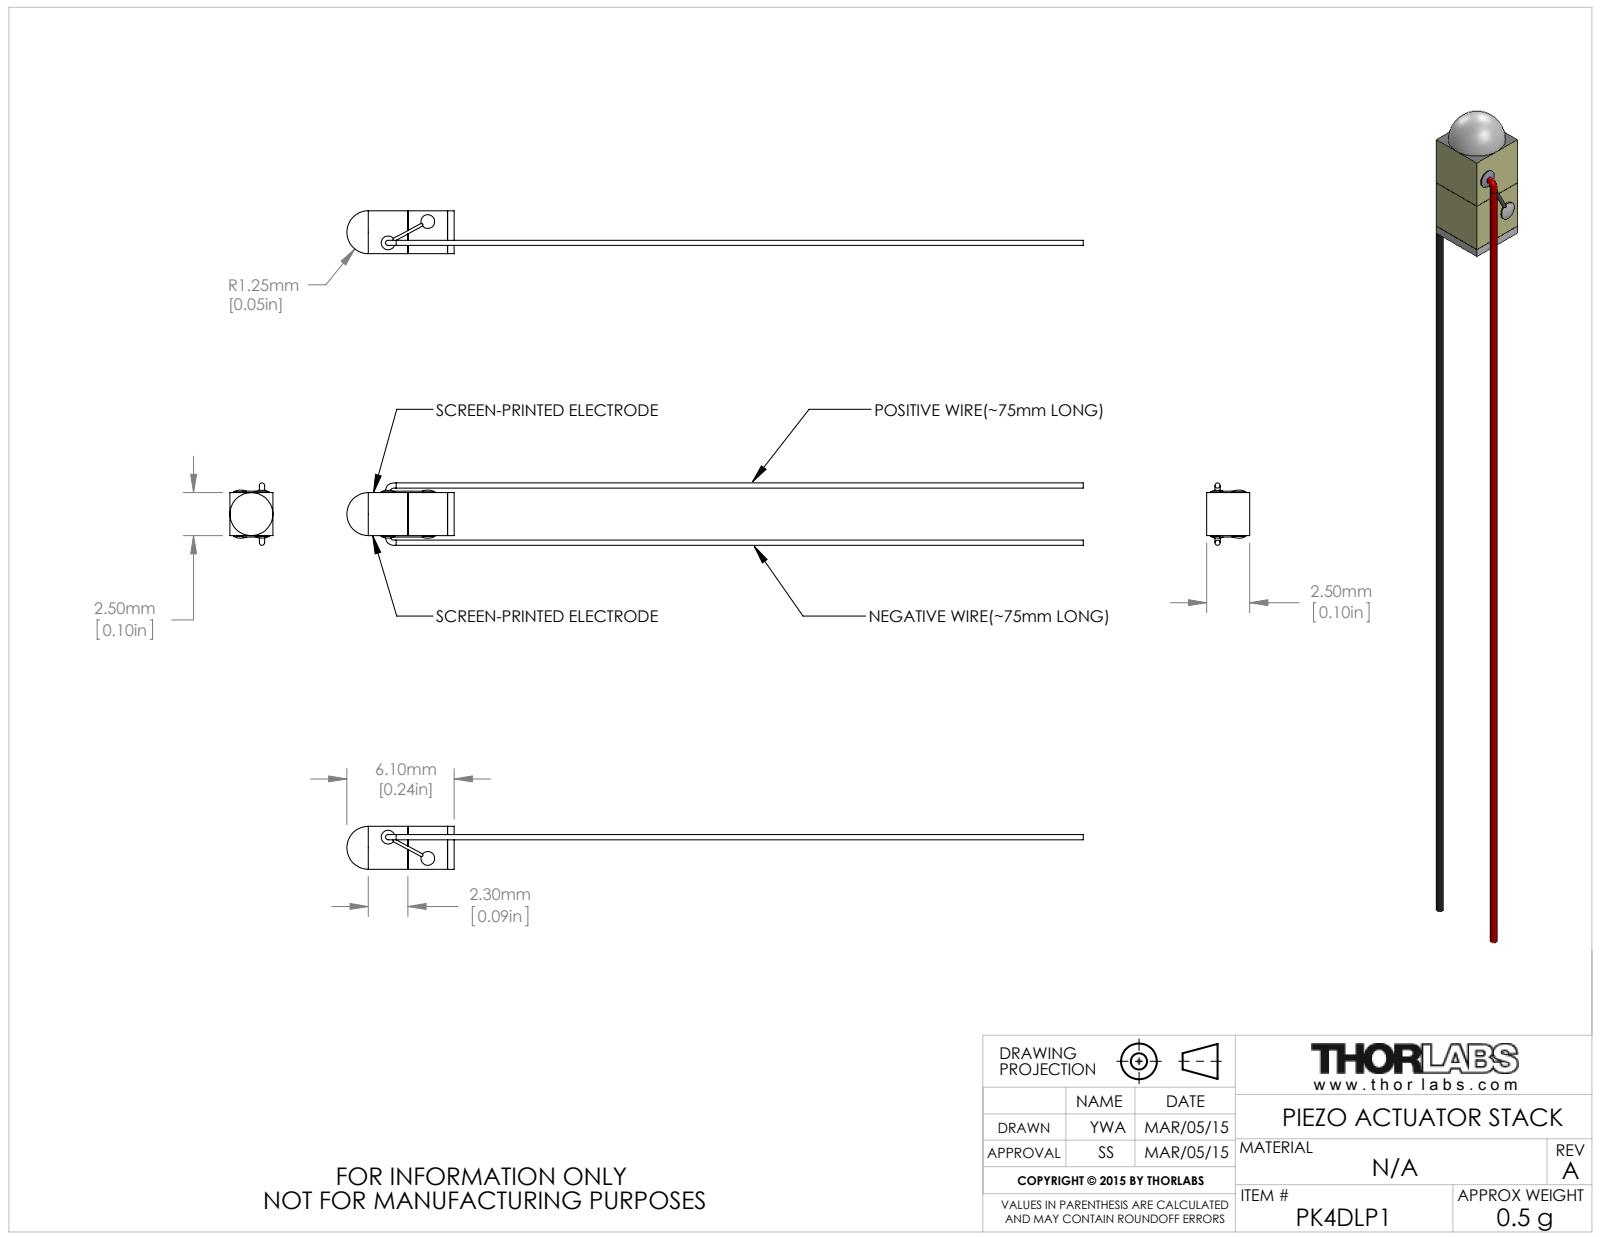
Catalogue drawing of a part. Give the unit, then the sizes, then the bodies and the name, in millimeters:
Units: millimetres
Overall size (bounding box): 42.87 × 3.63 × 2.5
Round bosses / shafts (diameter × count): ⌀0.8 ×2
Main face-to-face distances: 2.5, 2.31, 2.3, 0.37, 0.38, 2.68, 2.69, 2.32, 4.99, 4.62
Volume: 41 mm³ · Surface area: 170 mm²
Bodies: 2 solids, 57 faces (23 planar, 16 cylindrical, 18 other)
Part name (STEP PRODUCT): PK4DLP1
STEP written by: SolidWorks 2014 (AUTOMOTIVE_DESIGN)
